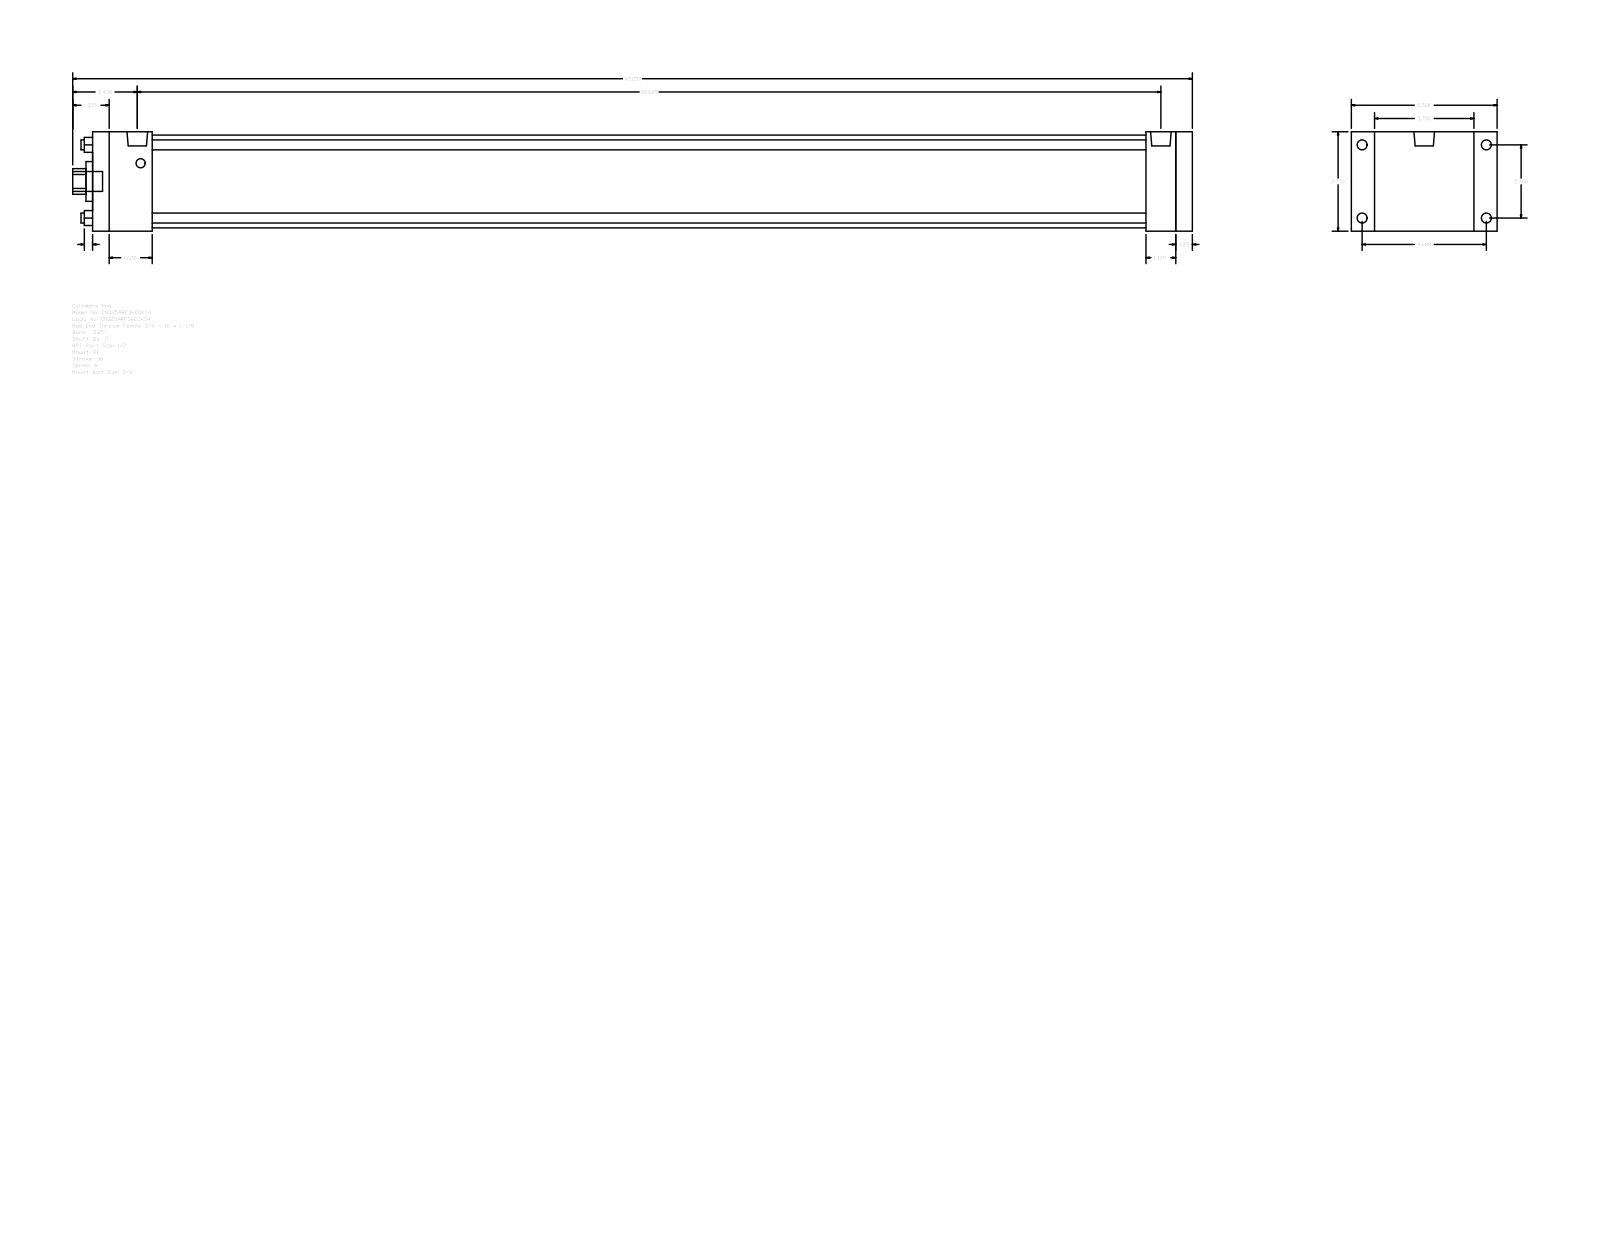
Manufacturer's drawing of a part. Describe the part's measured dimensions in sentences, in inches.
The part is named "A_RF__0325_1". Its 3-D file was written by "GSSL Pune (CONFIG_CONTROL_DESIGN)". It is 0 solids with 92 faces: 64 planar, 28 cylindrical and 0 other. Overall it measures 42.25 by 5.5 by 3.75 inches. Round holes: 4 of diameter 0.375, 1 of diameter 1, 1 of diameter 1.5, 1 of diameter 3.5. Round bosses or shafts: 4 of diameter 0.375, 4 of diameter 0.344, 2 of diameter 0.778, 1 of diameter 0.75. Partial cylindrical surfaces (rounded edges, fillets, slot ends): 1 of radius 0.484. The main face-to-face distances are 3.75, 41.5, 0.625, 40.875, 0.875, 4.625, 39.75, 1.125, 1.75, 2.25. The hole center spacings are 1.952, 2.76, 3.903.
